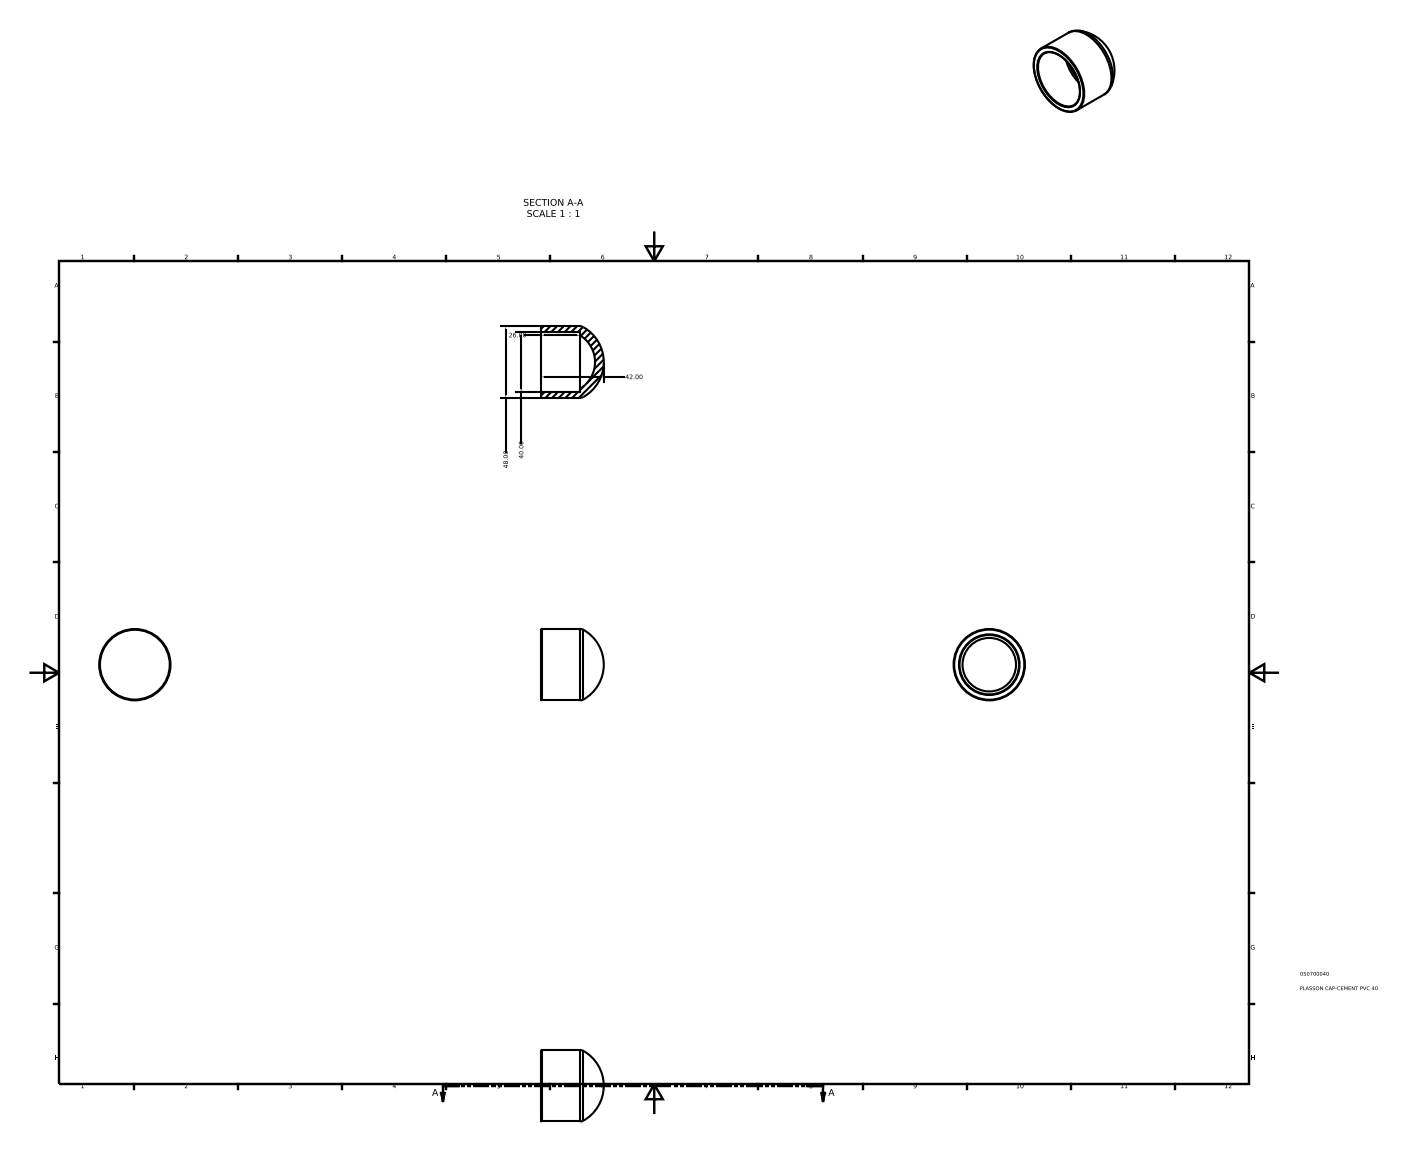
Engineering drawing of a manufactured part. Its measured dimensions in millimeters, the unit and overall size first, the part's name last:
Units: millimetres
Overall size (bounding box): 48 × 48 × 42
Round holes (diameter × count): ⌀40 ×1
Round bosses / shafts (diameter × count): ⌀48 ×1
Main face-to-face distances: 26
Volume: 25 973 mm³ · Surface area: 11 949 mm²
Bodies: 1 solid, 9 faces (2 planar, 2 cylindrical, 5 other)
Part name (STEP PRODUCT): 050700040
STEP written by: Autodesk Inventor 2015 (AUTOMOTIVE_DESIGN)
